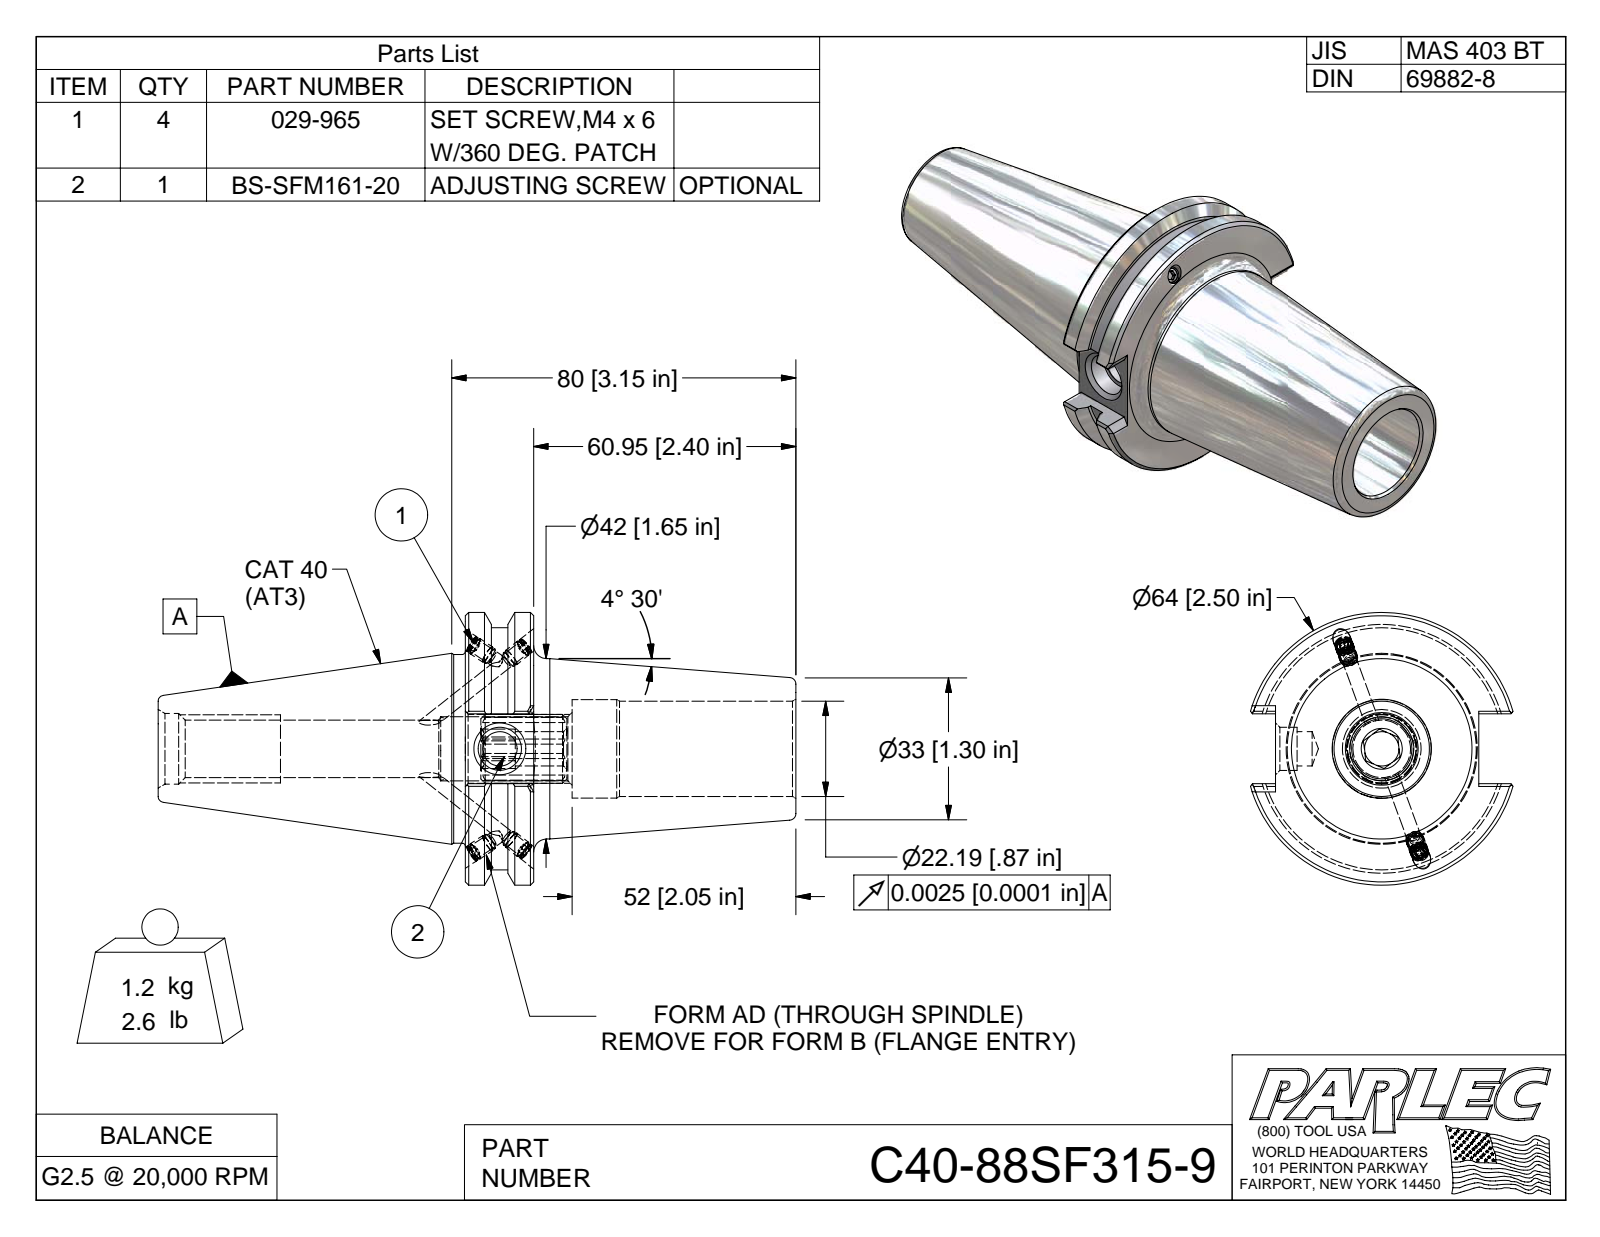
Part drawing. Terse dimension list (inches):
name: C40-88SF315-9; C40BC-88SF315-9-1; 029-965; BS-SFM161-20
written by: Autodesk Inventor 2009 (AUTOMOTIVE_DESIGN)
unit: in
bodies: 6 solids, 173 faces (87 planar, 32 cylindrical, 54 other)
size: 5.837 × 2.5 × 2.403
volume: 9.079 in³; area: 52.35 in²
holes: 4× ⌀0.13, 4× ⌀0.161, 1× ⌀0.874, 1× ⌀0.904
bosses: 4× ⌀0.165, 4× ⌀0.157, 1× ⌀2.5, 1× ⌀2.219, 1× ⌀1.73, 1× ⌀1.654
rounds: 1× R0.315
face distances: 0.625, 3.025, 2.4, 0.978, 0.352, 2.047, 0.64, 0.551, 1.86, 2.812
